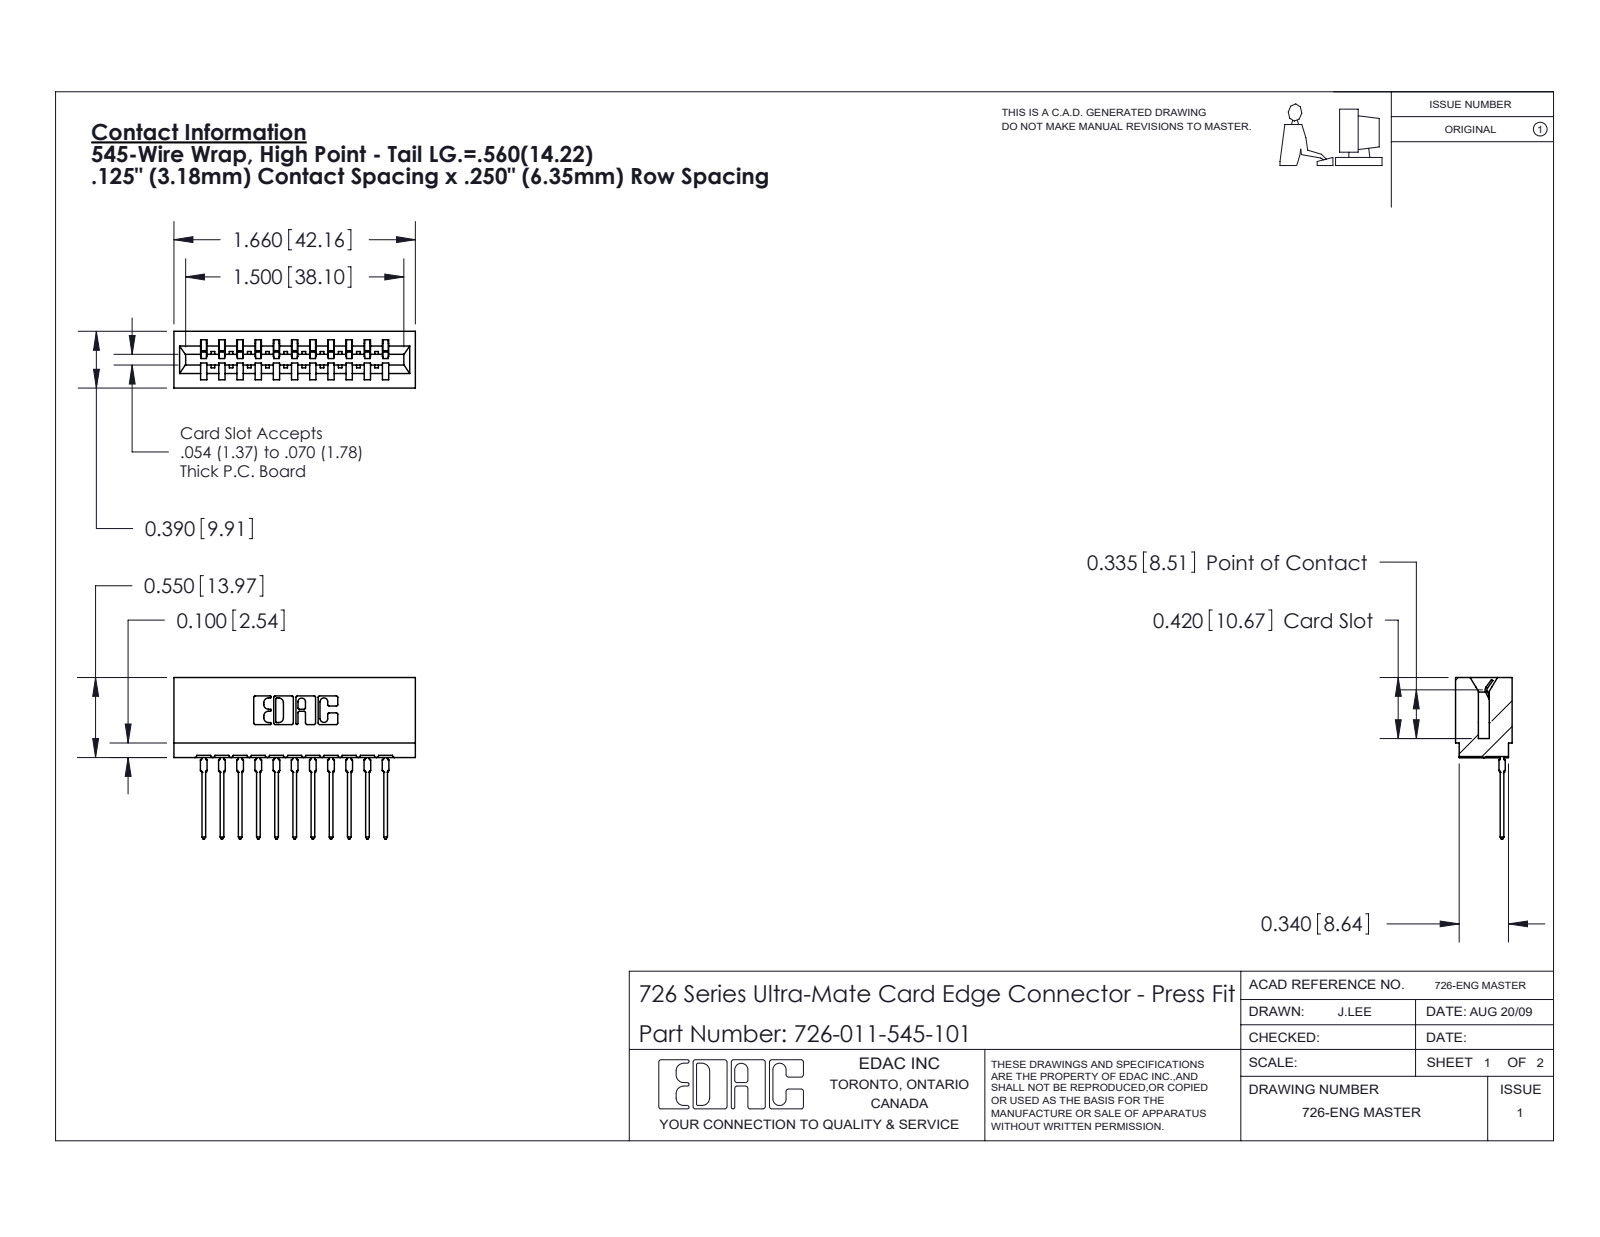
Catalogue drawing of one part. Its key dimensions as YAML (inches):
part_name: "726 Part_.515 Slot Depth - 01; 726-011-545-101; 746-292-001_545"
step_written_by: "SolidWorks 2020 (CONFIG_CONTROL_DESIGN)"
units: inches
bodies: {solids: 12, faces: 1285, planar: 748, cylindrical: 251, other: 286}
overall_size: [1.66, 1.109, 0.39]
volume: 0.242
surface_area: 8.929
partial_cylinders:
  - {radius: 0.01, count: 22}
  - {radius: 0.021, count: 22}
  - {radius: 0.015, count: 12}
  - {radius: 0.007, count: 6}
  - {radius: 0.031, count: 6}
  - {radius: 0.005, count: 4}
  - {radius: 0.011, count: 4}
  - {radius: 0.026, count: 3}
face_to_face_distances: [0.25, 0.333, 0.057, 0.5, 0.75, 0.042, 0.125, 0.125, 0.083, 0.39]
